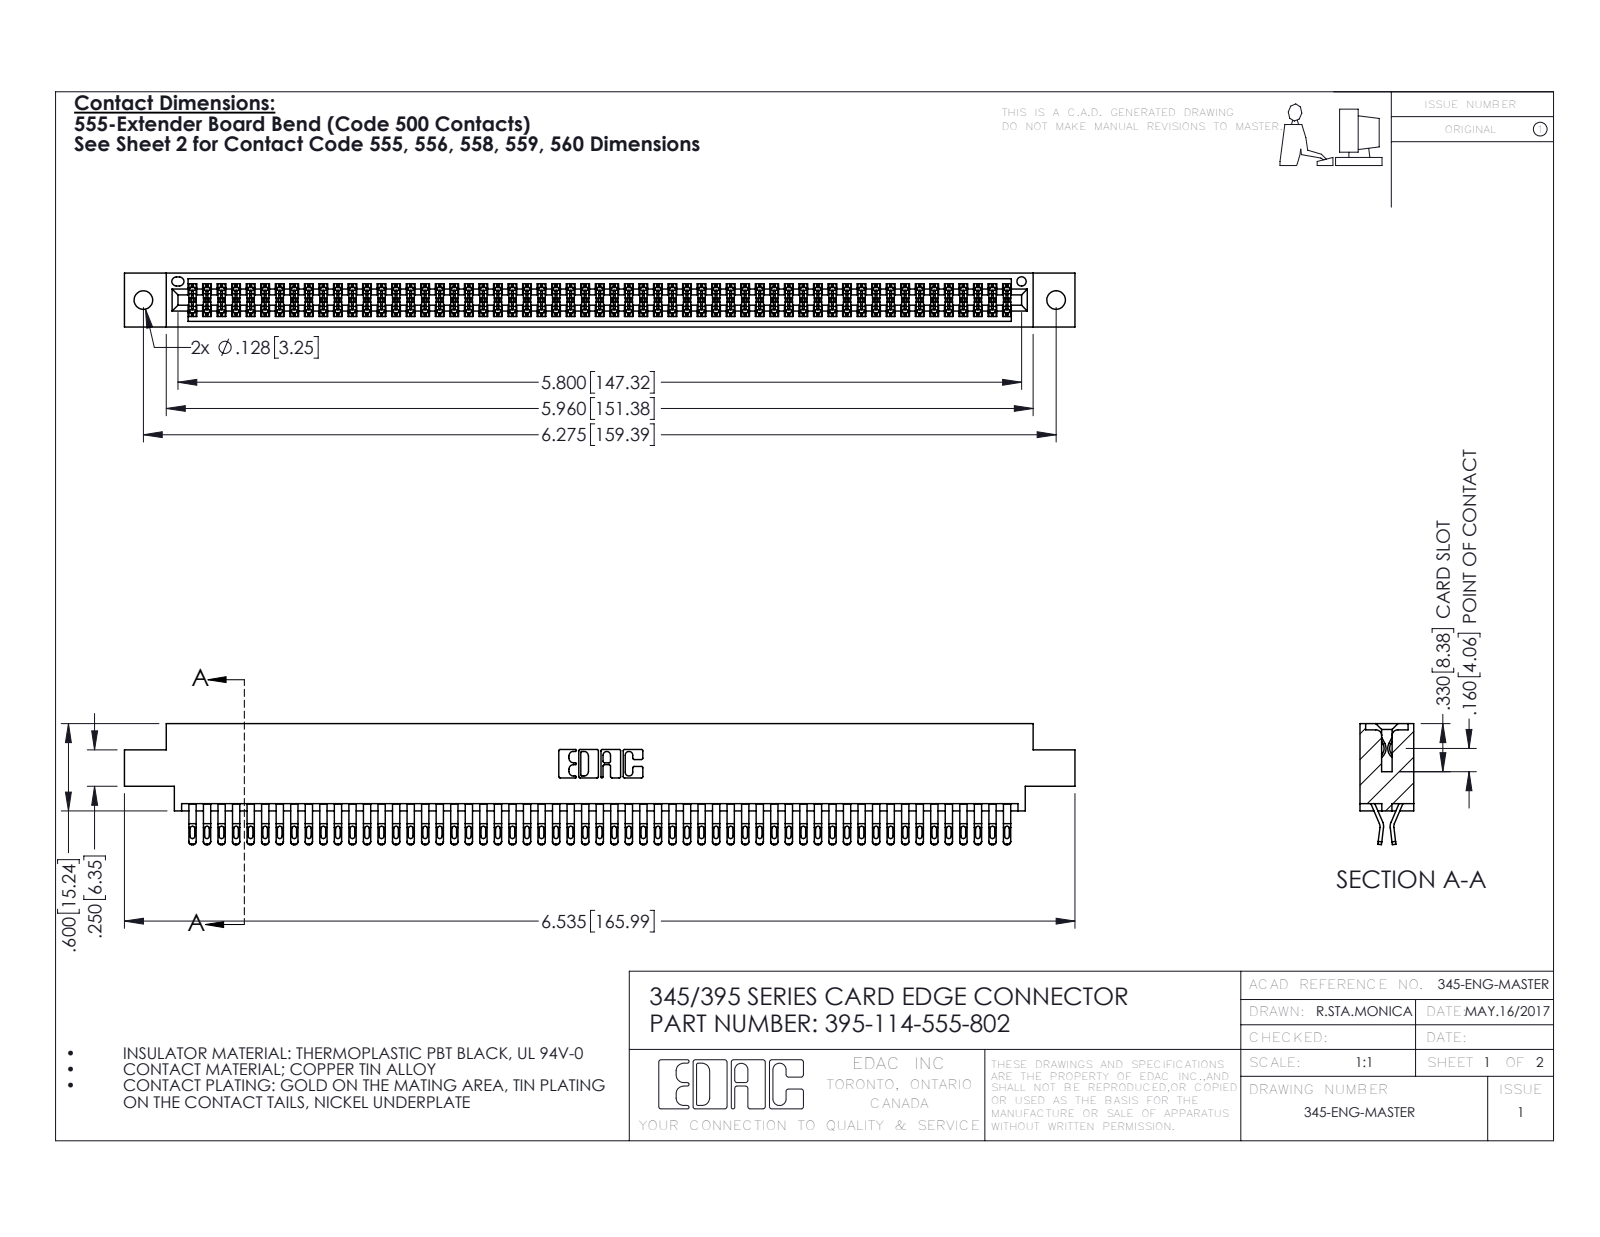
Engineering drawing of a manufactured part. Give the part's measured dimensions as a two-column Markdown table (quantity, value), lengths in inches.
| quantity | value |
| --- | --- |
| part name | 395-114-555-802; 345-292-001_555 Tail; 345 Part_0.170 Offset - 0.128 Dia |
| STEP written by | SolidWorks 2016 (CONFIG_CONTROL_DESIGN) |
| units | inches |
| bodies | 115 solids, 6514 faces (3618 planar, 2896 cylindrical, 0 other) |
| overall size | 6.535 × 0.832 × 0.37 |
| volume | 1.003 in³ |
| surface area | 39.71 in² |
| round holes (diameter × count) | 0.128 × 2, 0.064 × 1 |
| partial cylindrical surfaces (radius × count) | 0.016 × 285, 0.02 × 228, 0.006 × 171, 0.01 × 22, 0.007 × 6, 0.031 × 6, 0.026 × 3, 0.01 × 2 |
| main face-to-face distances | 0.298, 0.072, 0.37, 0.025, 0.2, 0.098, 0.272, 0.225, 0.175, 0.149 |
| hole center spacings | 0.27, 6.039, 6.275 |
